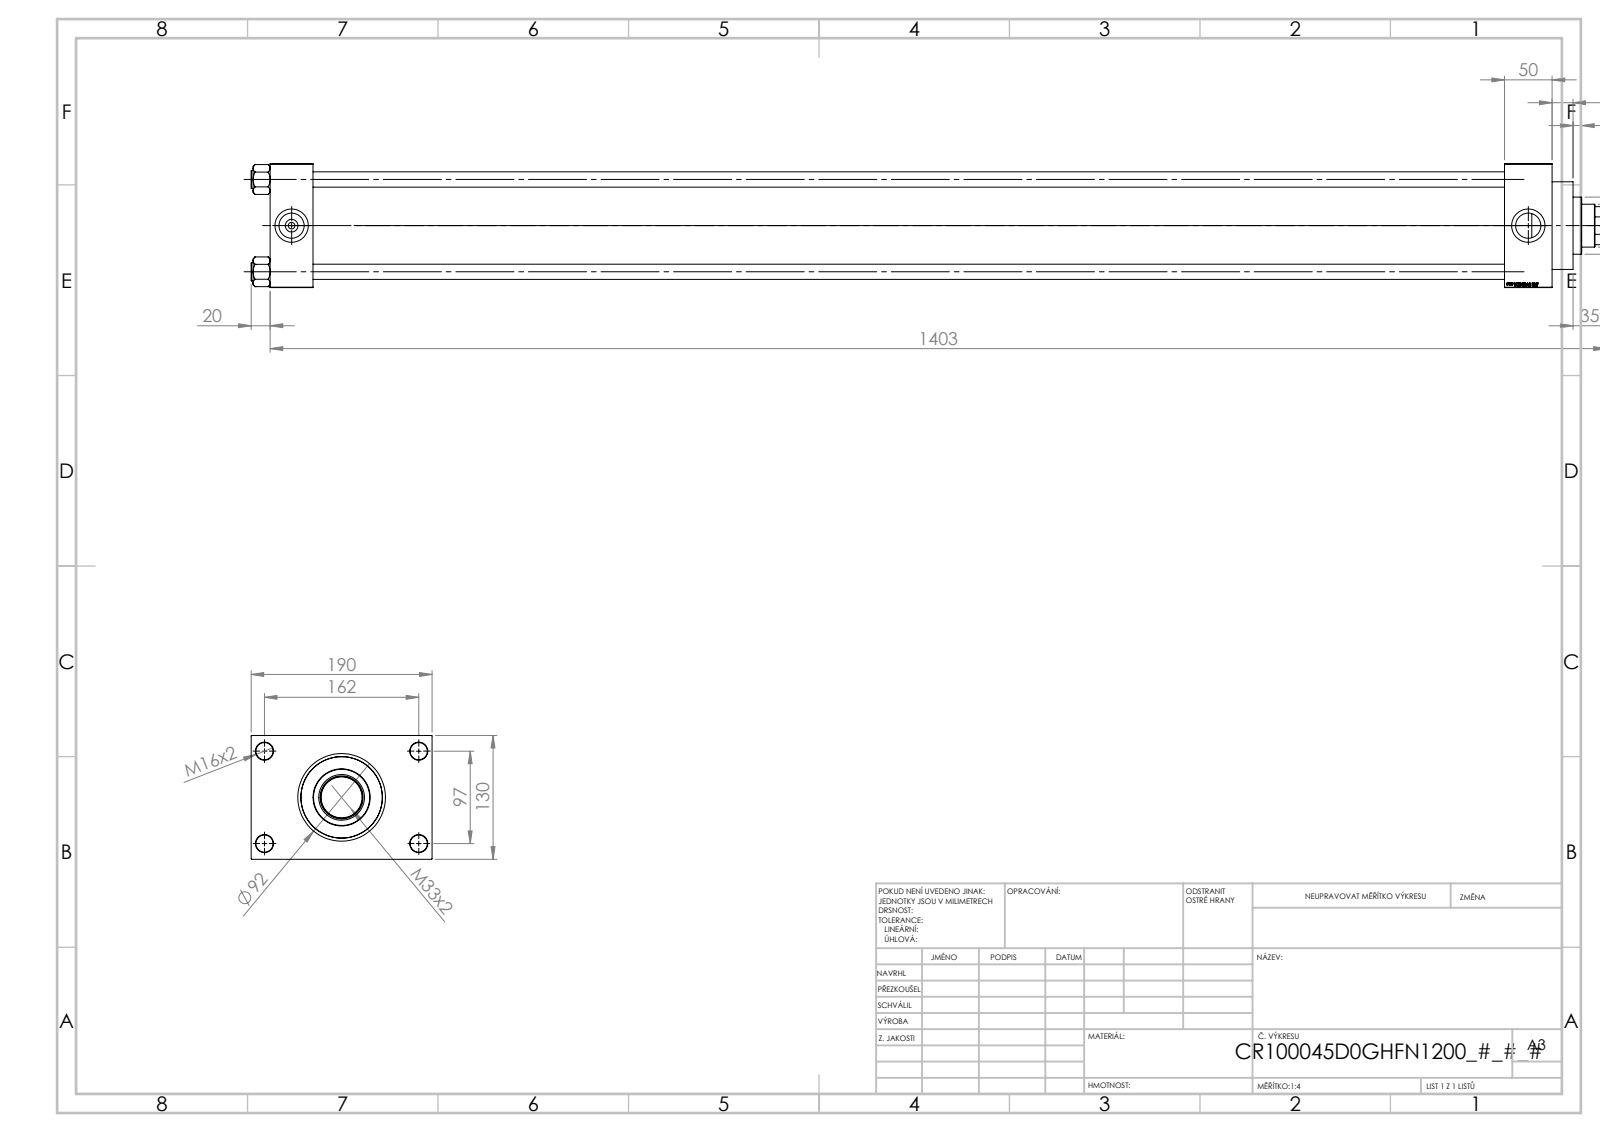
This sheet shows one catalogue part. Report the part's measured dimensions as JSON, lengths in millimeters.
{"part_name": "V215CR_D_TYCINKA; V215CR_VCP_D; V215CR_ROD_END_F; V215_VC_A (+2 more)", "step_written_by": "SolidWorks 2019 (CONFIG_CONTROL_DESIGN)", "units": "millimeters", "bodies": {"solids": 12, "faces": 1172, "planar": 550, "cylindrical": 96, "other": 526}, "overall_size": [1467, 190, 130], "volume_mm3": 6614000, "surface_area_mm2": 1531000, "round_holes": [[16, 4], [18, 4], [2.5, 2], [7, 2], [26.44, 2], [35, 2], [31.5, 1], [45, 1], [48, 1], [76, 1], [85.5, 1], [100, 1]], "round_bosses_or_shafts": [[19, 4], [106, 1], [92, 1], [60, 1], [44, 1], [33, 1]], "face_to_face_distances": [130, 45, 1296, 1251, 1346, 1301, 50, 30, 160, 96], "hole_center_spacings": [32.55, 49.02, 62.87, 68.52, 94.41, 96.9, 101.73, 102.27]}
